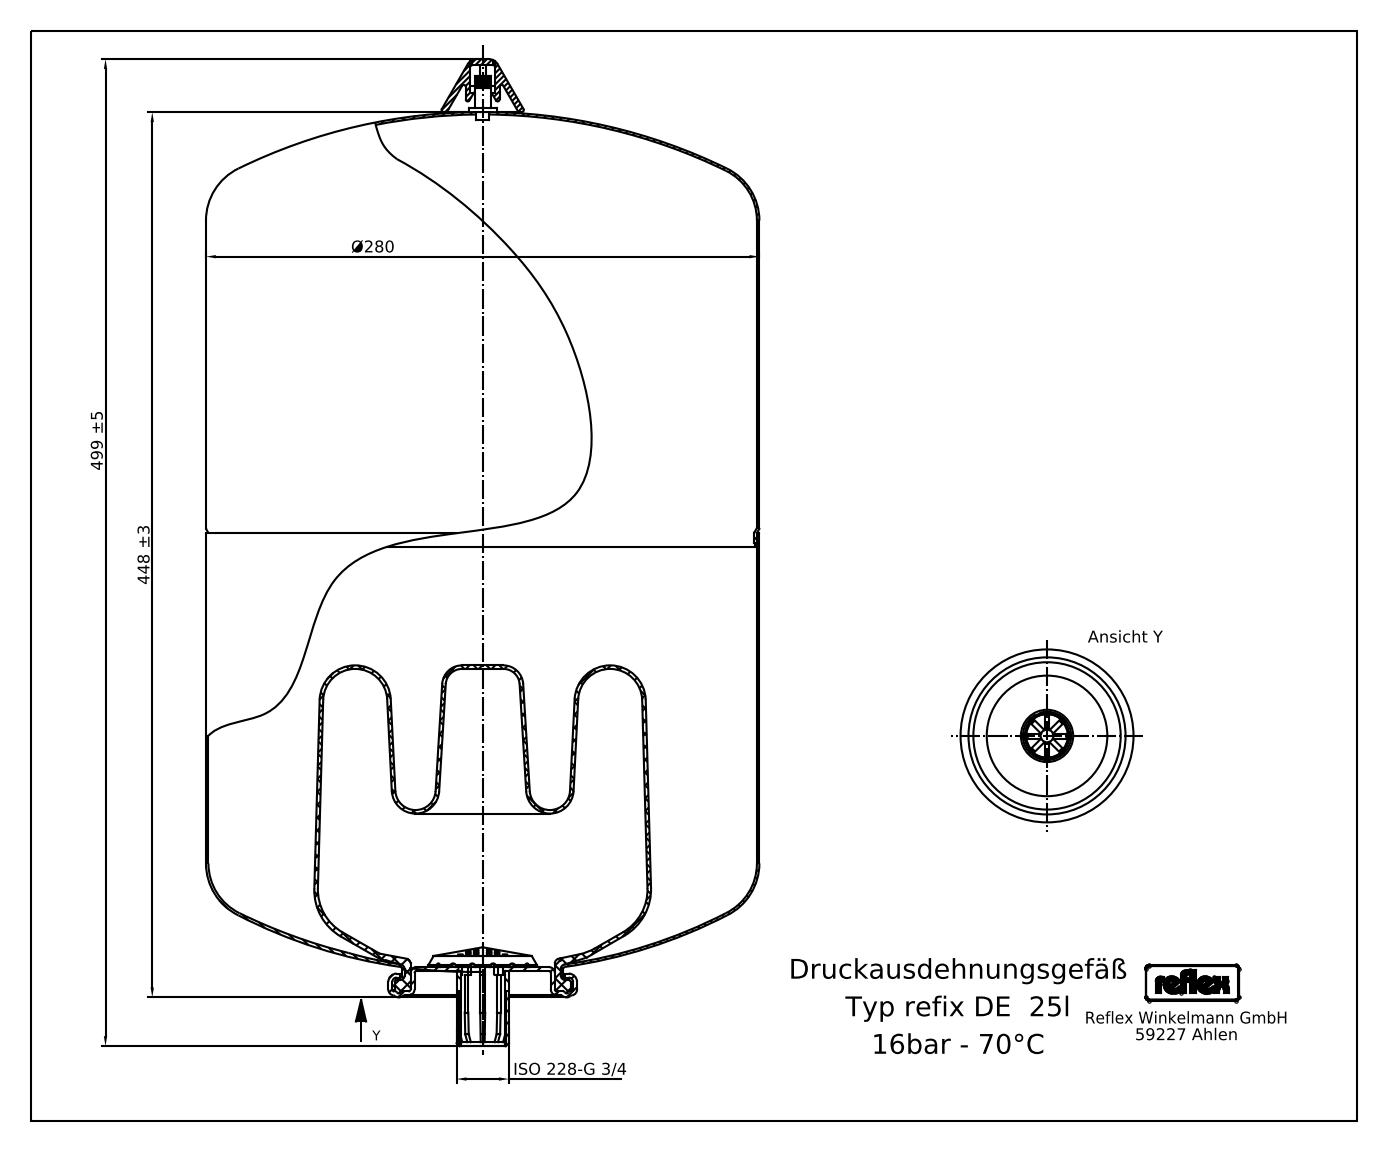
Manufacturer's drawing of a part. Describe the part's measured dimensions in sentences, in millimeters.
Its 3-D file was written by "Mechanical Desktop 2008 (CONFIG_CONTROL_DESIGN)". It is 13 solids with 151 faces: 71 planar, 46 cylindrical and 34 other. Overall it measures 499 by 280.32 by 280 millimeters. Its volume is 24 520 000 cubic millimeters and its surface area 723 254 square millimeters. Round holes: 1 of diameter 14.1, 1 of diameter 18.9. Round bosses or shafts: 1 of diameter 280, 1 of diameter 96, 1 of diameter 82, 1 of diameter 26.9, 1 of diameter 17.1, 1 of diameter 9, 1 of diameter 6. Partial cylindrical surfaces (rounded edges, fillets, slot ends): 4 of radius 1.12, 3 of radius 0.45, 2 of radius 0.77, 2 of radius 1.35, 2 of radius 1.85, 2 of radius 1.88, 2 of radius 2.54, 1 of radius 0.56. The main face-to-face distances are 325, 49, 374, 13, 62, 387, 224, 211, 162, 163.
